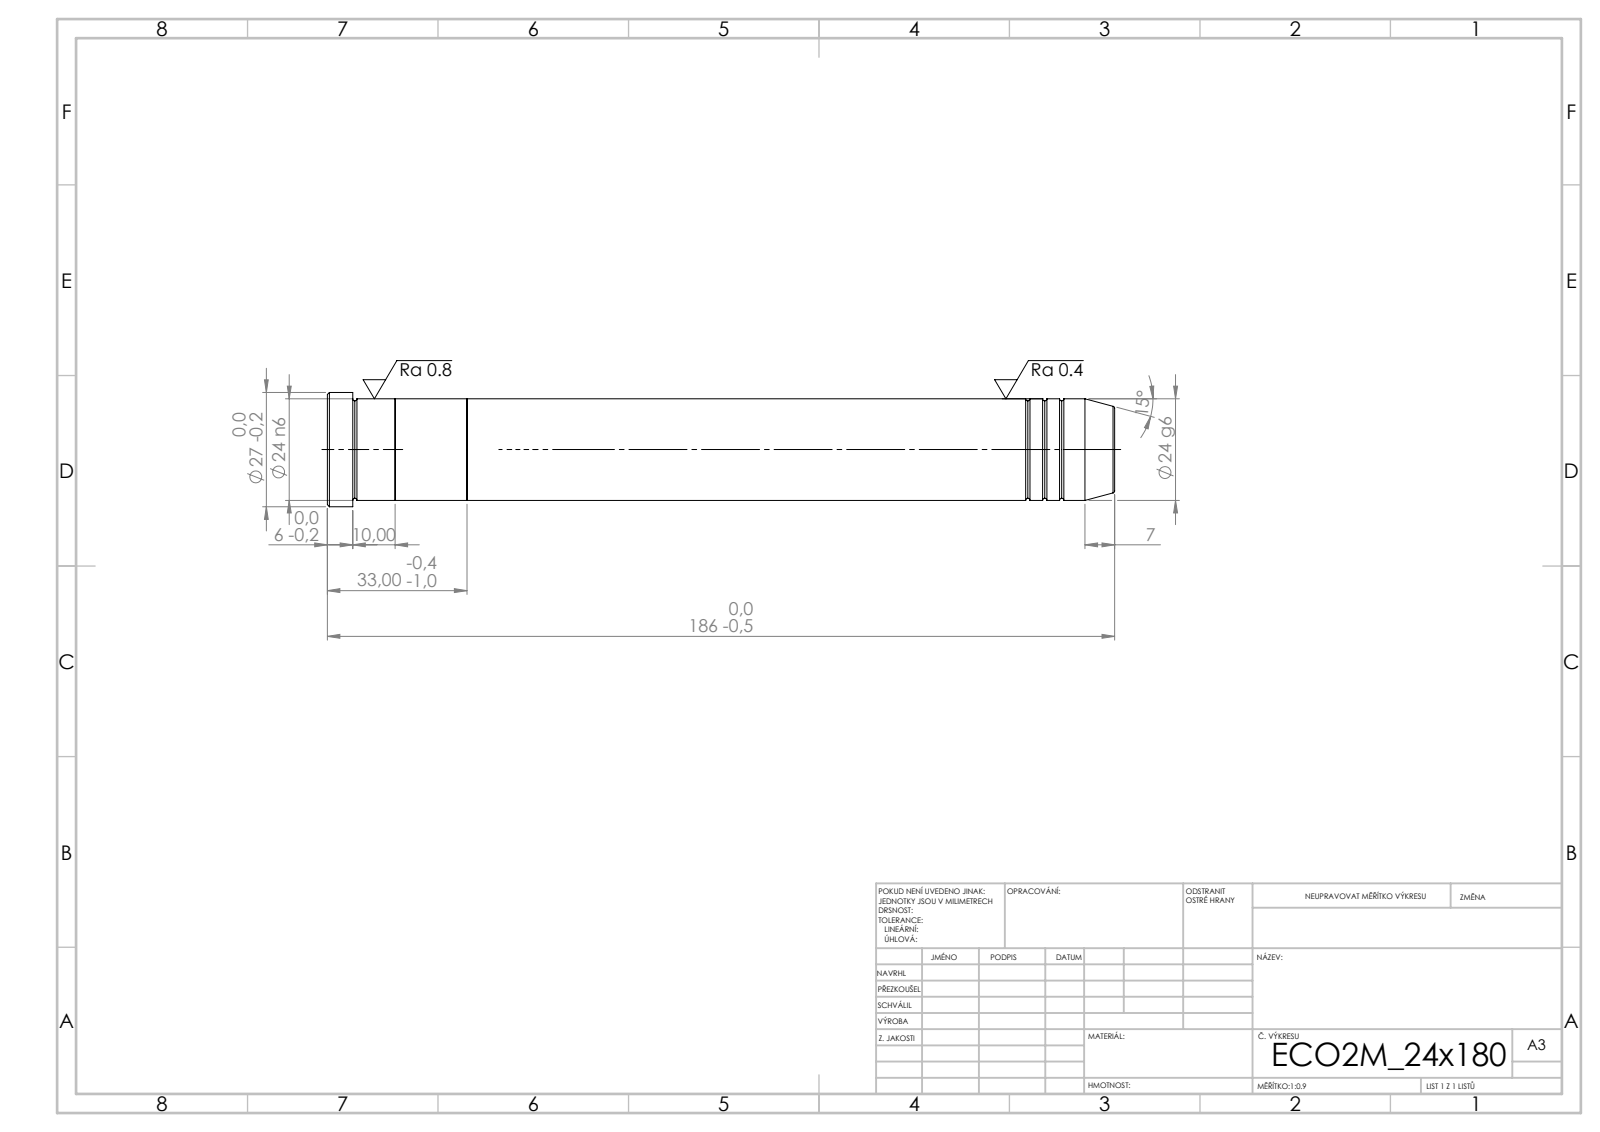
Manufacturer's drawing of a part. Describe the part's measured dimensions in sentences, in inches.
Its 3-D file was written by "SolidWorks 2019 (CONFIG_CONTROL_DESIGN)". It is 3 solids with 43 faces: 7 planar, 14 cylindrical and 22 other. Overall it measures 7.323 by 1.063 by 1.063 inches. Its volume is 5.142 cubic inches and its surface area 26.36 square inches. Round bosses or shafts: 1 of diameter 1.063, 1 of diameter 0.945. The main face-to-face distances are 0.669, 1.299, 0.63, 6.024, 6.693, 7.323, 7.087, 1.063, 0.394, 0.236.
